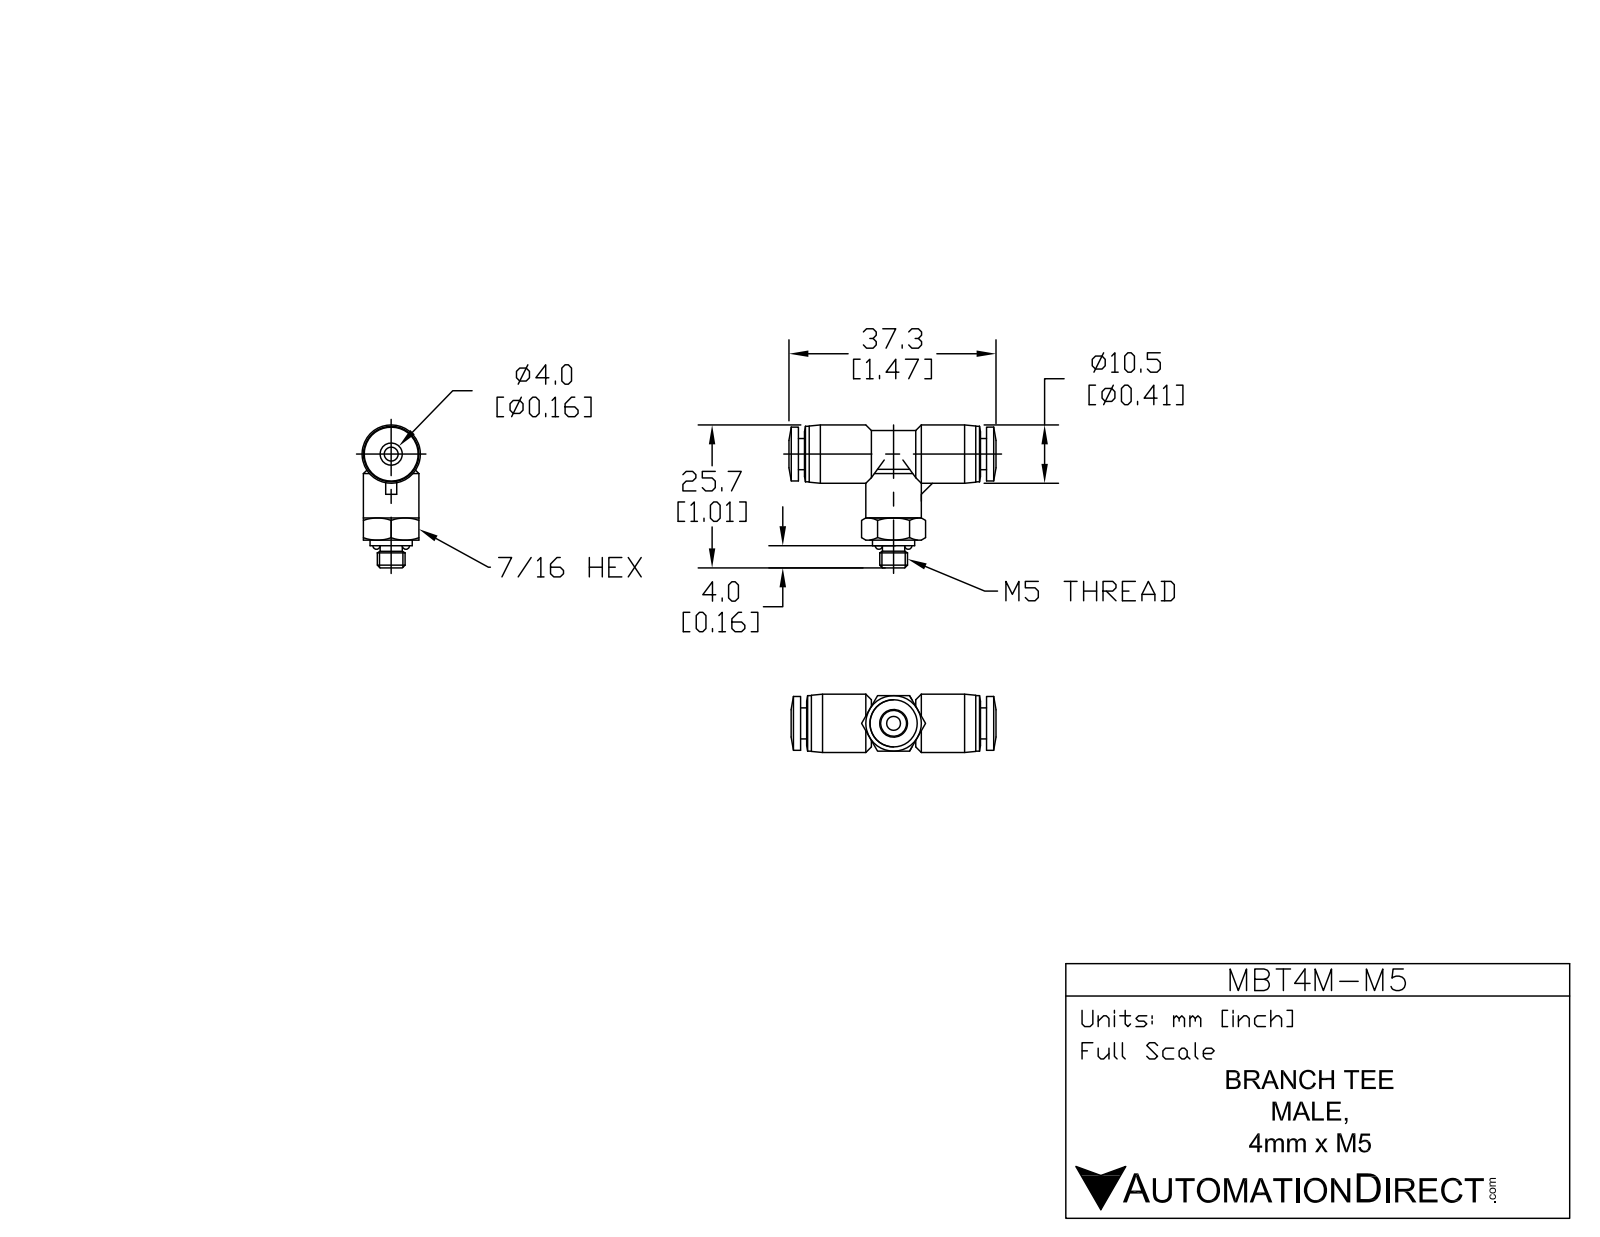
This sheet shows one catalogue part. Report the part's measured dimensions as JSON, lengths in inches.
{"part_name": "MBT4M-M5", "step_written_by": "SolidWorks 2015 (AUTOMOTIVE_DESIGN)", "units": "inches", "bodies": {"solids": 2, "faces": 118, "planar": 27, "cylindrical": 41, "other": 50}, "overall_size": [1.453, 1.014, 0.413], "volume_in3": 0.194, "surface_area_in2": 4.113, "round_holes": [[0.098, 2], [0.169, 1]], "round_bosses_or_shafts": [[0.394, 2], [0.413, 1], [0.382, 1], [0.315, 1], [0.299, 1], [0.22, 1], [0.197, 1], [0.157, 1]], "partial_cylinders_radius": [[0.157, 1]], "face_to_face_distances": [0.394, 0.043, 1.276, 1.319, 1.232, 0.516, 0.803, 0.472, 0.76, 0.157]}
